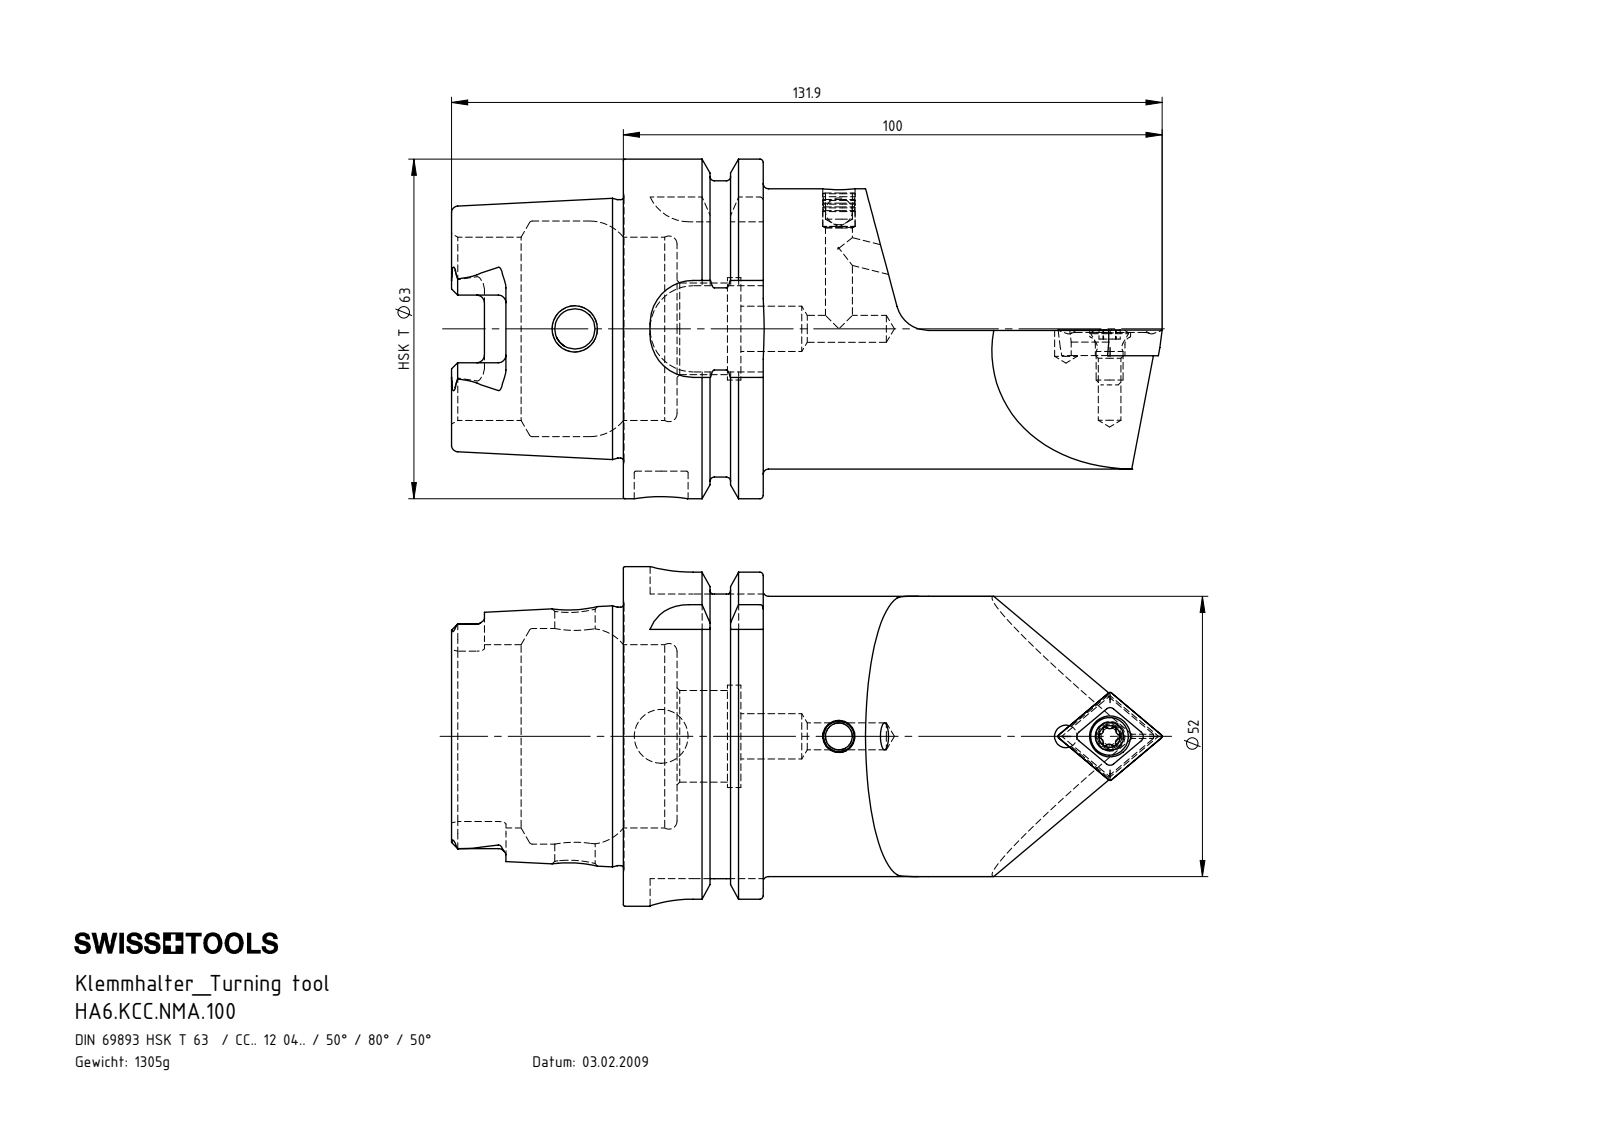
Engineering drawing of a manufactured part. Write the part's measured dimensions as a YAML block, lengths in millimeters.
part_name: "HA6-KCC.NMA.100; KVT_MB_600_060; WCC-ER2.001.010_A; CCMT120404 (+1 more)"
step_written_by: "SolidWorks 2012 (CONFIG_CONTROL_DESIGN)"
units: millimeters
bodies: {solids: 5, faces: 301, planar: 76, cylindrical: 90, other: 135}
overall_size: [131.9, 63, 63]
volume: 166251
surface_area: 32559
round_holes:
  - {diameter: 5, count: 3}
  - {diameter: 4.2, count: 2}
  - {diameter: 5.5, count: 1}
  - {diameter: 7.5, count: 1}
  - {diameter: 7.6, count: 1}
  - {diameter: 8.4, count: 1}
  - {diameter: 10, count: 1}
  - {diameter: 17, count: 1}
  - {diameter: 19, count: 1}
  - {diameter: 34, count: 1}
  - {diameter: 40, count: 1}
round_bosses_or_shafts:
  - {diameter: 63, count: 1}
  - {diameter: 54.95, count: 1}
  - {diameter: 52, count: 1}
  - {diameter: 47.94, count: 1}
  - {diameter: 7, count: 1}
  - {diameter: 6, count: 1}
  - {diameter: 5, count: 1}
partial_cylinders:
  - {radius: 0.39, count: 6}
  - {radius: 0.69, count: 6}
  - {radius: 1.4, count: 6}
  - {radius: 8, count: 4}
  - {radius: 2.82, count: 2}
  - {radius: 2.88, count: 2}
  - {radius: 6, count: 1}
face_to_face_distances: [25.95, 16, 9.95, 31.9, 41.85, 57.85, 52.8, 21.8, 11.85, 53.7]
hole_center_spacings: [8.1, 8.2, 33, 42.14, 50.24, 50.34, 75.14, 83.24]
